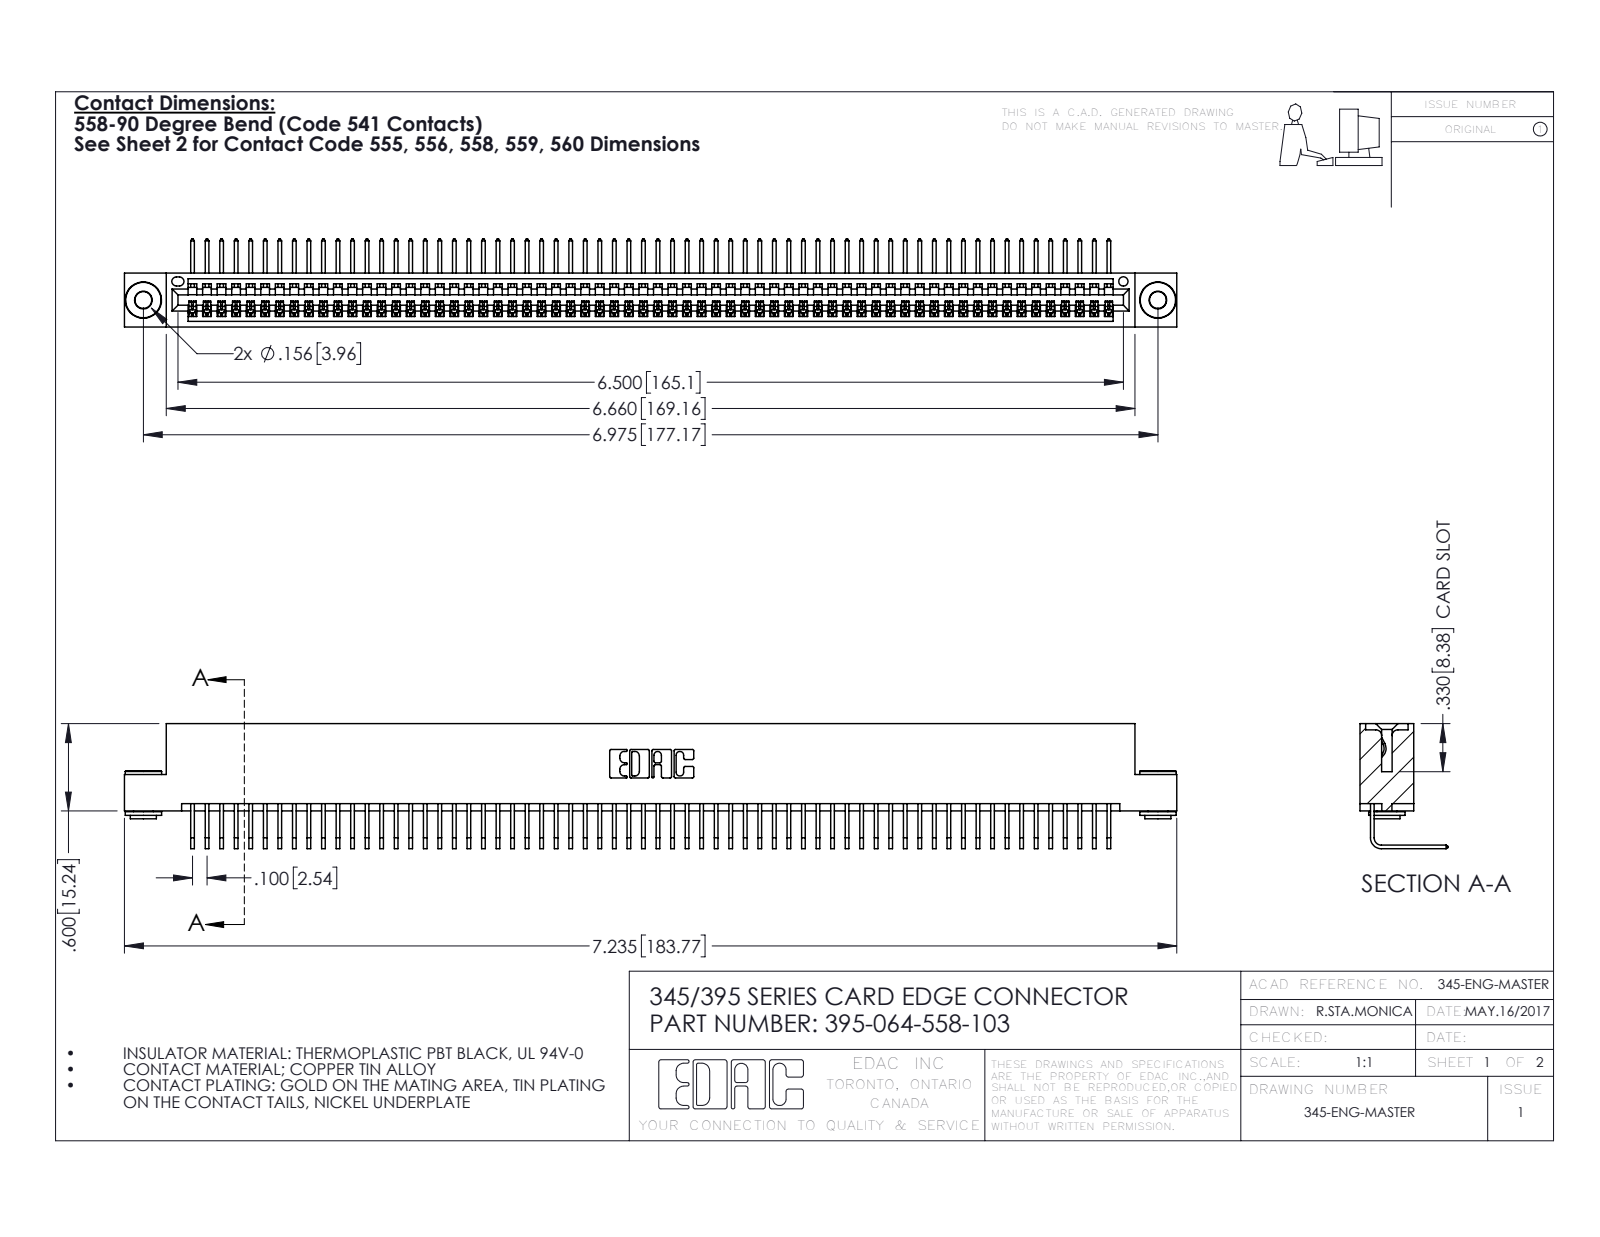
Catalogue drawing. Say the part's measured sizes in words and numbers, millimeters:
The part is named "345-250-002_345-250-002-102; 345-292-001_558 Tail - 2; 345 Part_Flush Mounting Lugs - 0.156 Dia-TH; 395-064-558-103". Its 3-D file was written by "SolidWorks 2016 (CONFIG_CONTROL_DESIGN)". It is 67 solids with 4004 faces: 2778 planar, 1218 cylindrical and 8 other. Overall it measures 183.8 by 21.8 by 15.4 millimeters. Its volume is 17 860 cubic millimeters and its surface area 25 510 square millimeters. Round holes: 2 of diameter 2.9, 2 of diameter 4, 1 of diameter 1.6. Round bosses or shafts: 2 of diameter 6.4, 2 of diameter 4.6, 2 of diameter 3.5. Partial cylindrical surfaces (rounded edges, fillets, slot ends): 128 of radius 0.2, 22 of radius 0.3, 6 of radius 0.2, 6 of radius 0.8, 3 of radius 0.7, 2 of radius 0.8, 2 of radius 1, 1 of radius 0.4. The main face-to-face distances are 1.8, 7.6, 9.4, 5.1, 0.6, 2.5, 6.9, 5.7, 3.8, 1.8. The hole center spacings are 6.9, 171.2, 177.2.
